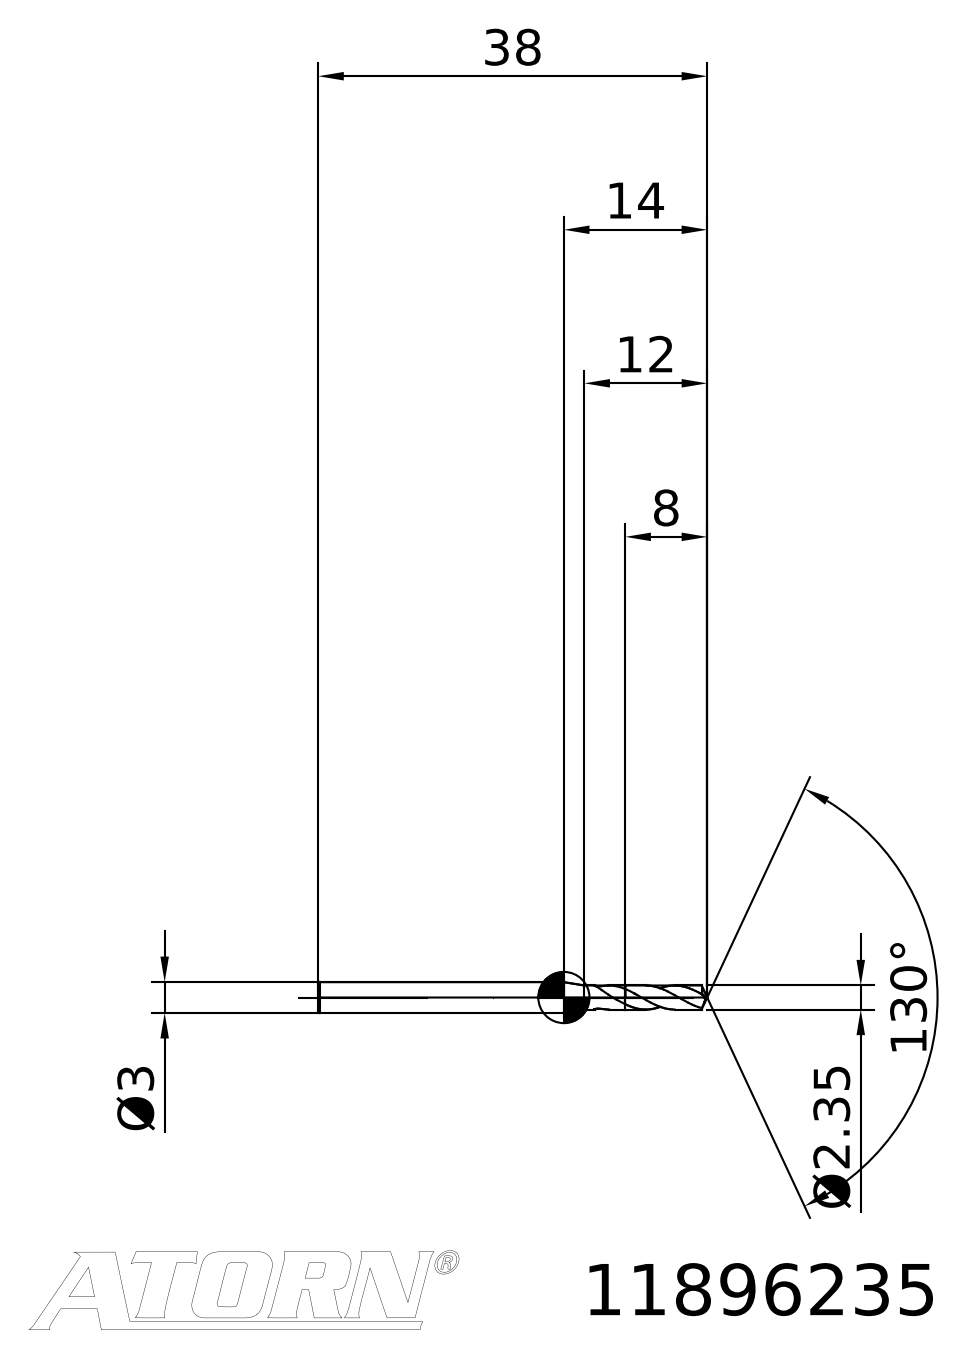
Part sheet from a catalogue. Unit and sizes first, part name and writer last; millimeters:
Units: millimetres
Overall size (bounding box): 38 × 3.83 × 3
Main face-to-face distances: 30
Volume: 217 mm³ · Surface area: 350 mm²
Bodies: 2 solids, 25 faces (3 planar, 0 cylindrical, 22 other)
STEP written by: TDM (AUTOMOTIVE_DESIGN)
